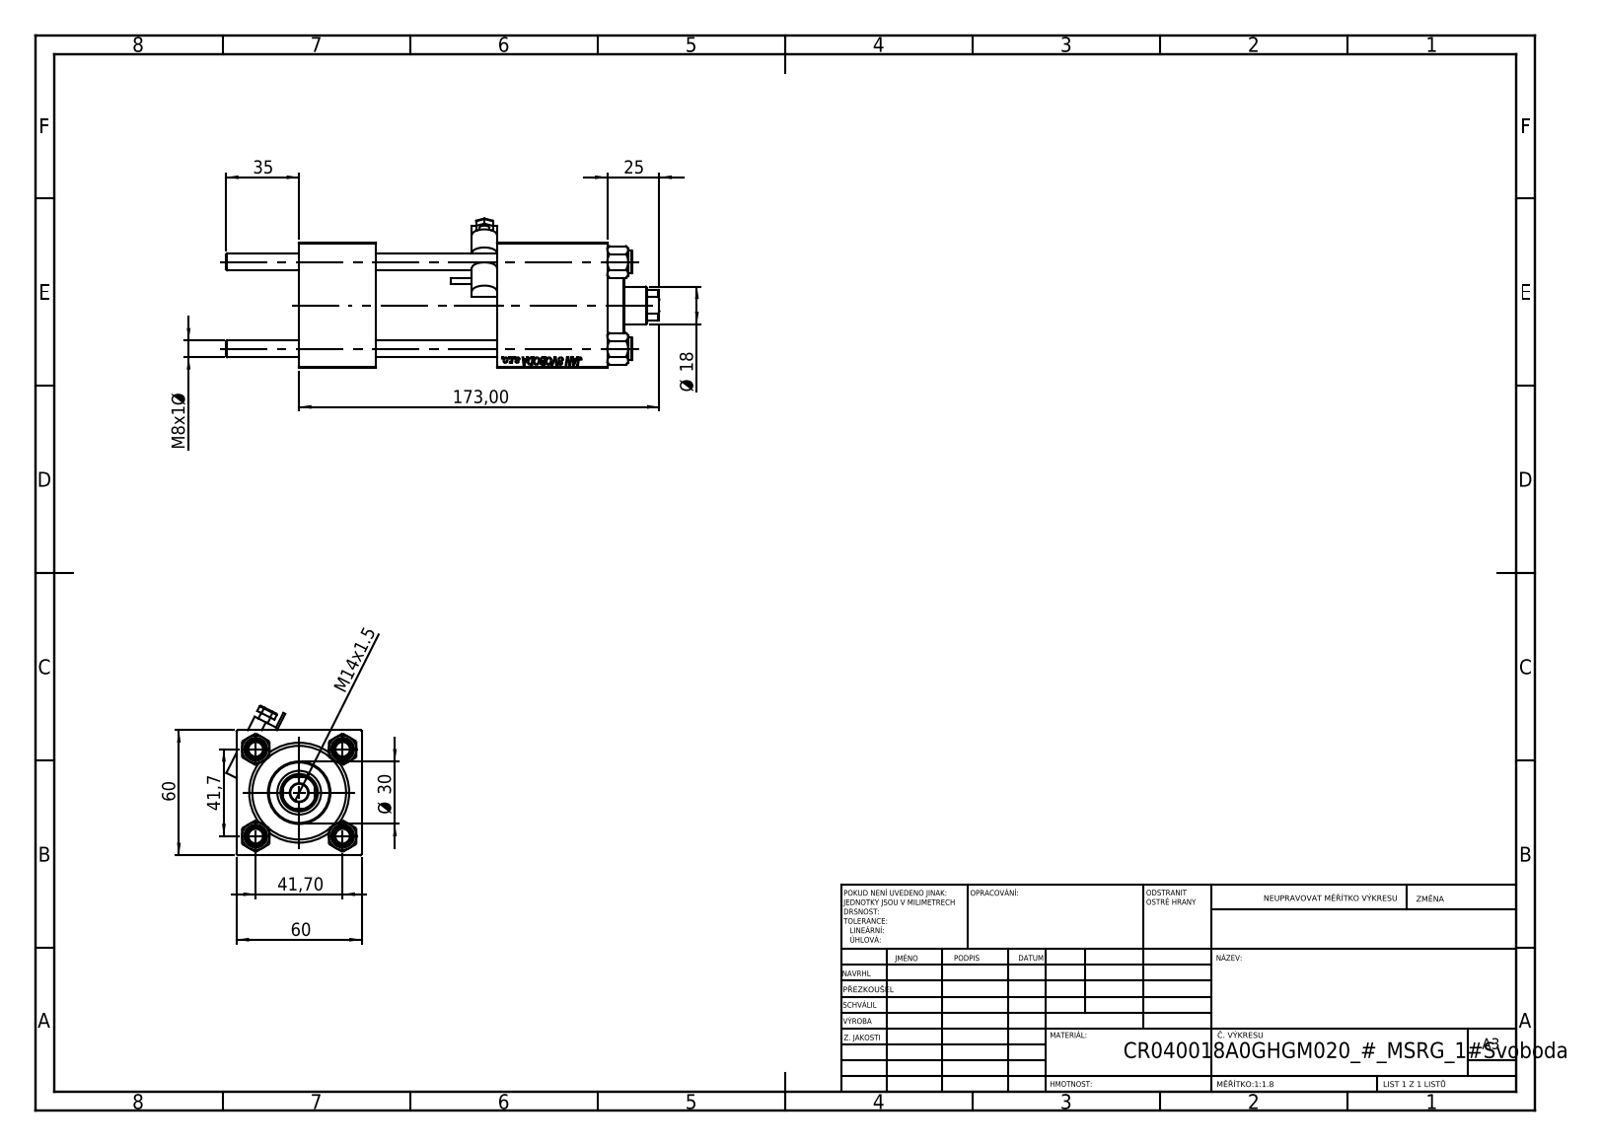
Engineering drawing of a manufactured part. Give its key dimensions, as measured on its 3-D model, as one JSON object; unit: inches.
{"part_name": "CR025_012_A_0_G_A_G_M_020_+#_##_TYCINKA; V215CR_VCP; V215_VC_A; NUT_M5 (+2 more)", "step_written_by": "SolidWorks 2019 (CONFIG_CONTROL_DESIGN)", "units": "inches", "bodies": {"solids": 12, "faces": 1167, "planar": 539, "cylindrical": 92, "other": 536}, "overall_size": [8.189, 2.824, 2.558], "volume_in3": 25.47, "surface_area_in2": 180, "round_holes": [[0.315, 4], [0.276, 2], [0.656, 2], [0.945, 2], [0.335, 1], [0.709, 1], [0.827, 1], [1.22, 1], [1.575, 1], [1.772, 1]], "round_bosses_or_shafts": [[0.433, 4], [1.811, 1], [1.181, 1], [0.197, 1], [0.098, 1]], "partial_cylinders_radius": [[0.02, 6], [0.236, 2], [0.335, 1]], "face_to_face_distances": [2.362, 1.457, 5.827, 4.37, 2.283, 2.087, 3.74, 4.697, 3.24, 0.957], "hole_center_spacings": [1.161, 1.642, 2.322, 3.642]}
